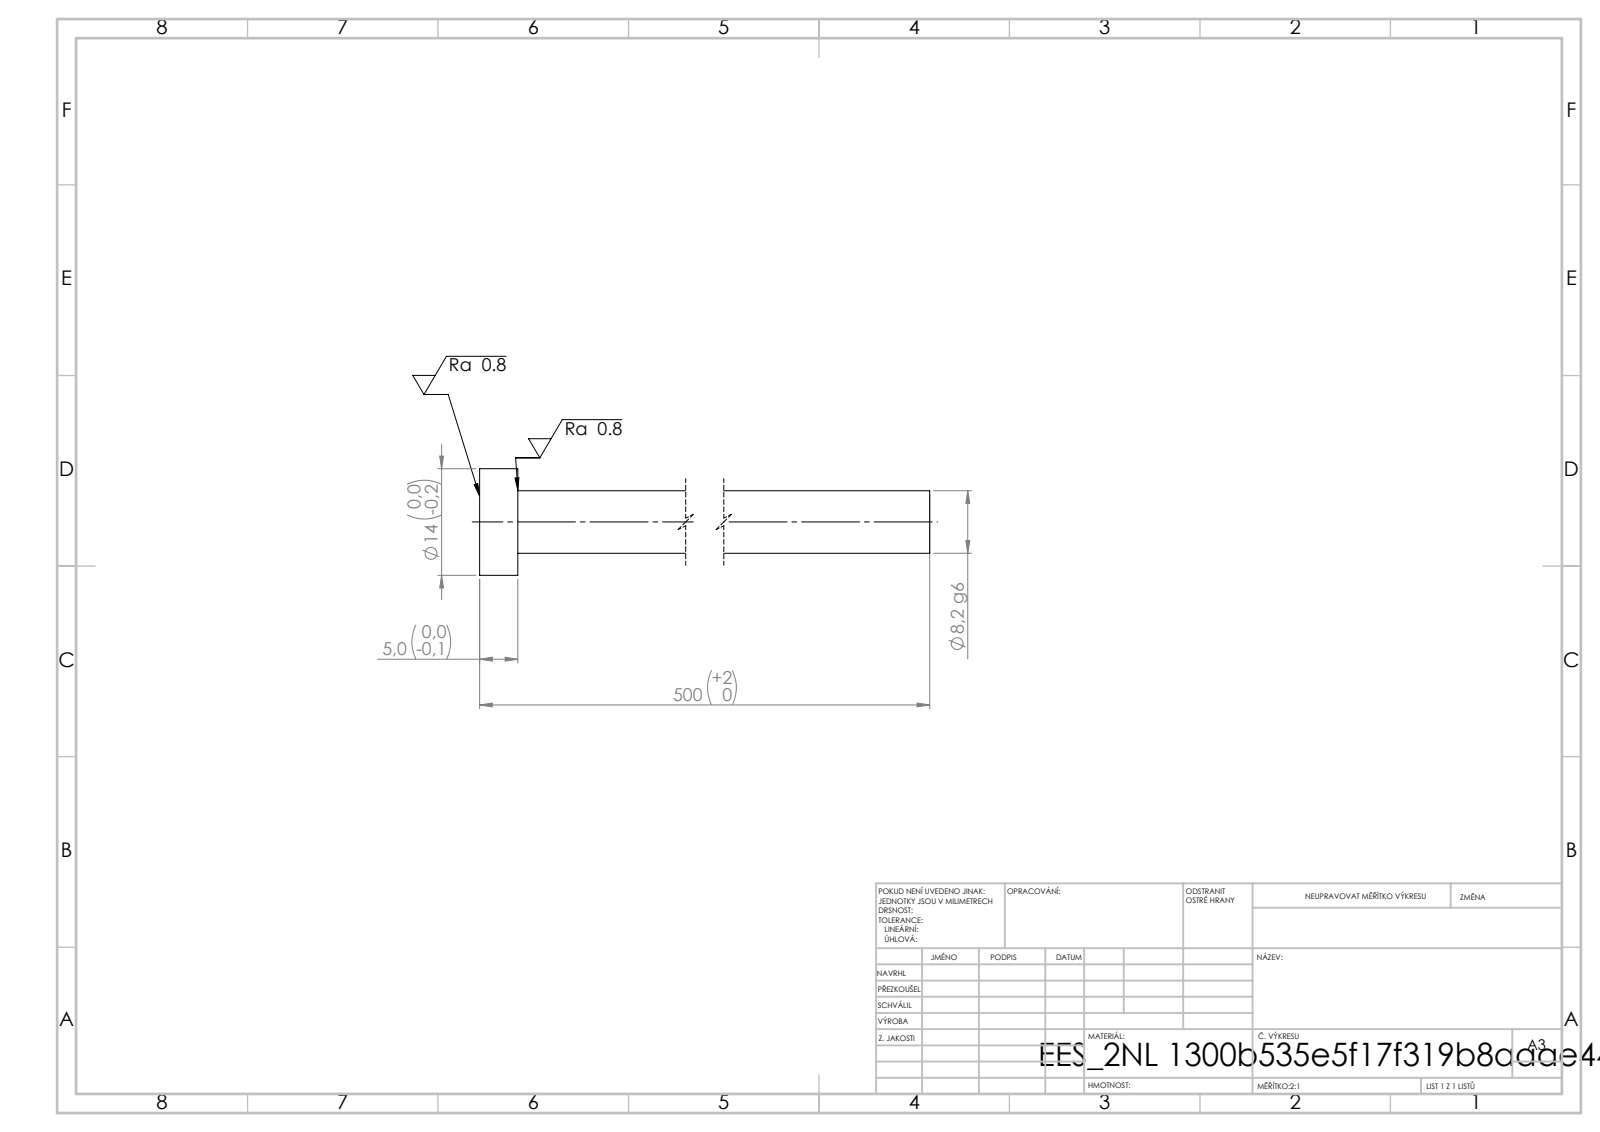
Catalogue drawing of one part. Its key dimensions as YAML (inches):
step_written_by: "SolidWorks 2019 (CONFIG_CONTROL_DESIGN)"
units: inches
bodies: {solids: 1, faces: 7, planar: 3, cylindrical: 4, other: 0}
overall_size: [19.685, 0.551, 0.551]
volume: 1.642
surface_area: 20.58
round_bosses_or_shafts:
  - {diameter: 0.551, count: 1}
  - {diameter: 0.323, count: 1}
face_to_face_distances: [0.197, 19.685, 19.488]
